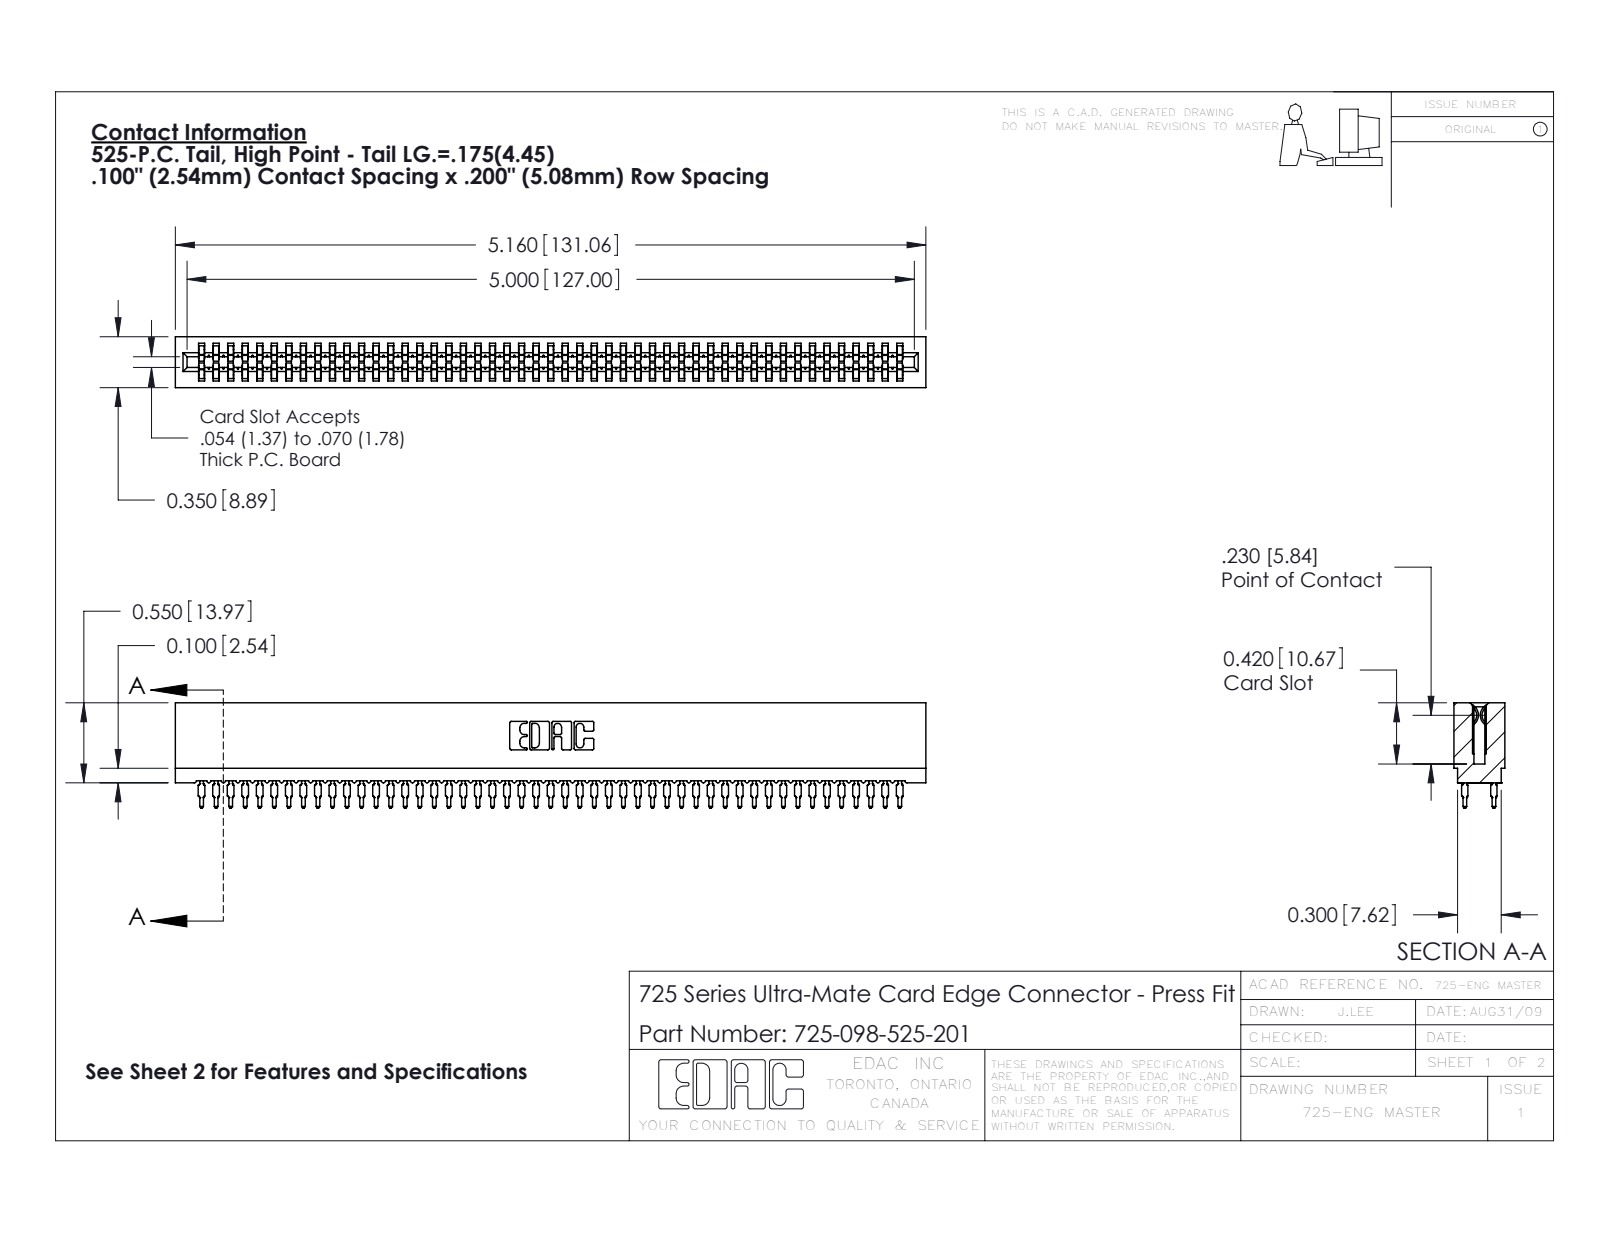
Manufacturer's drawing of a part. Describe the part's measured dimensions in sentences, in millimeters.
The part is named "725-098-525-201; 745-292-001_525; 725 Part_Insulator Option - 01". Its 3-D file was written by "SolidWorks 2016 (CONFIG_CONTROL_DESIGN)". It is 99 solids with 8866 faces: 4563 planar, 1755 cylindrical and 2548 other. Overall it measures 131.1 by 18.4 by 8.9 millimeters. Its volume is 10 300 cubic millimeters and its surface area 21 810 square millimeters. Partial cylindrical surfaces (rounded edges, fillets, slot ends): 196 of radius 0.5, 98 of radius 0.4, 22 of radius 0.3, 8 of radius 0.1, 8 of radius 0.3, 6 of radius 0.2, 6 of radius 0.8, 3 of radius 0.7. The main face-to-face distances are 1.6, 7.3, 5.1, 8.9, 5.4, 3.5, 1.9, 3.8, 7.7, 1.1.
